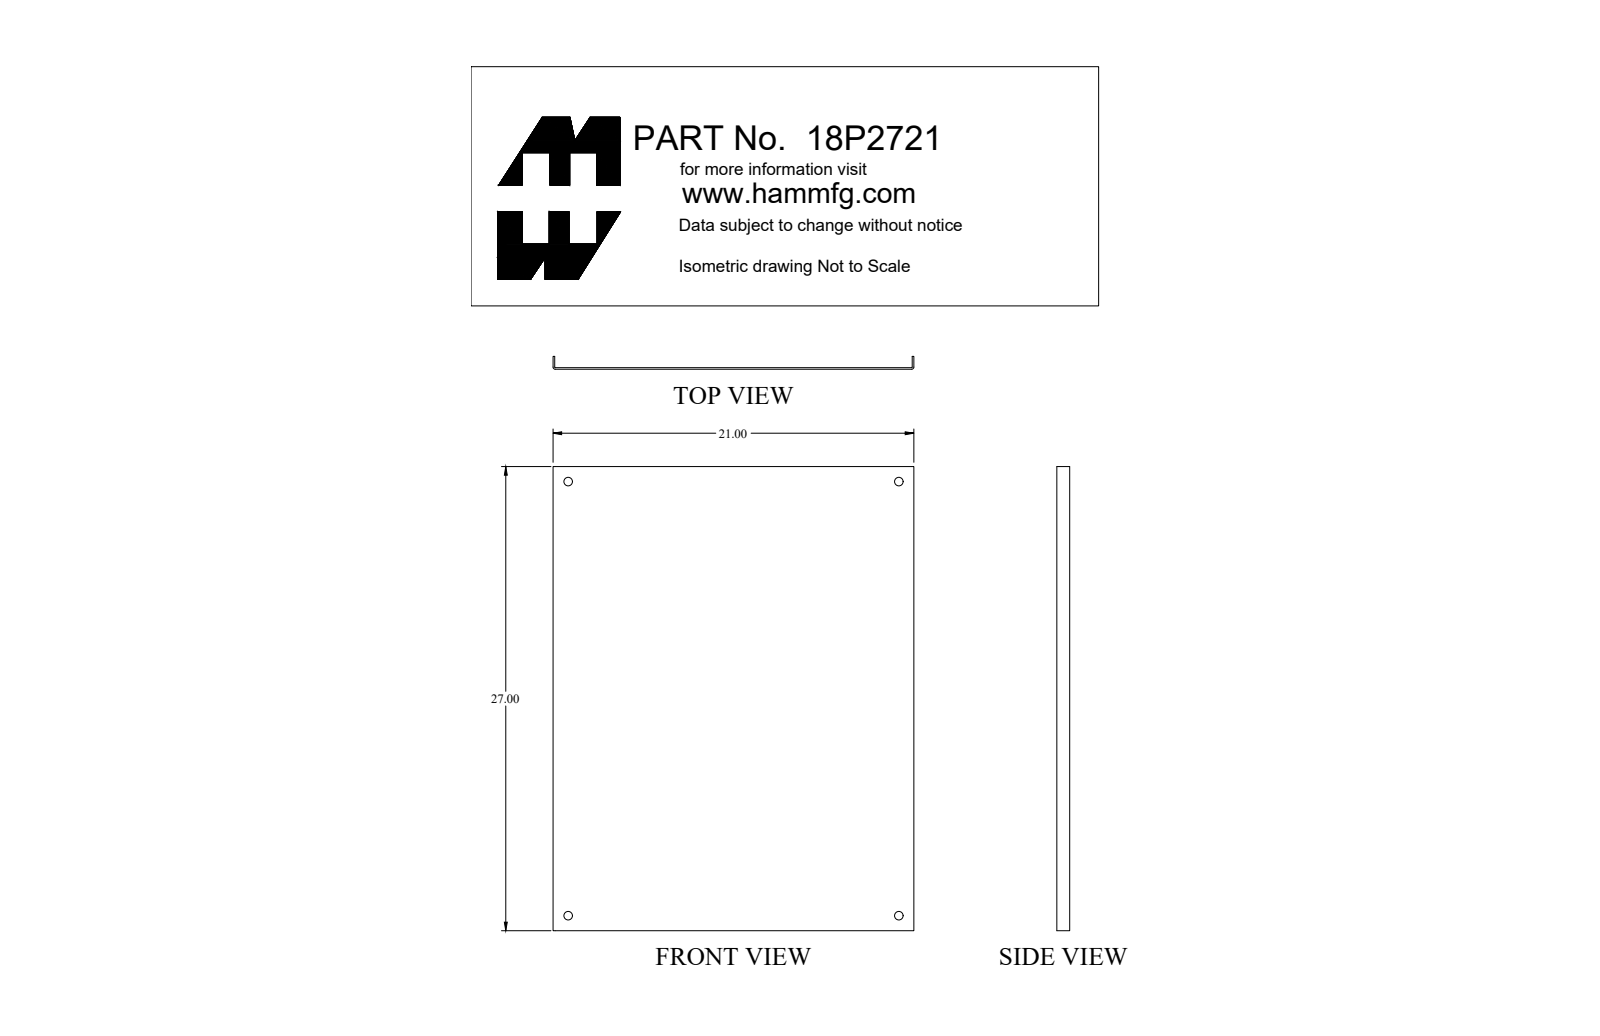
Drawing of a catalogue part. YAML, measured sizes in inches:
part_name: "18P2721_Default"
step_written_by: "SolidWorks 2018 (CONFIG_CONTROL_DESIGN)"
units: inches
bodies: {solids: 1, faces: 22, planar: 10, cylindrical: 12, other: 0}
overall_size: [27, 21, 0.75]
volume: 56.98
surface_area: 1210
round_holes:
  - {diameter: 0.5, count: 4}
partial_cylinders:
  - {radius: 0.03, count: 2}
  - {radius: 0.125, count: 2}
face_to_face_distances: [0.095, 20.905, 21, 20.81, 0.75, 0.655, 27]
hole_center_spacings: [19.25, 25.25, 31.751]
